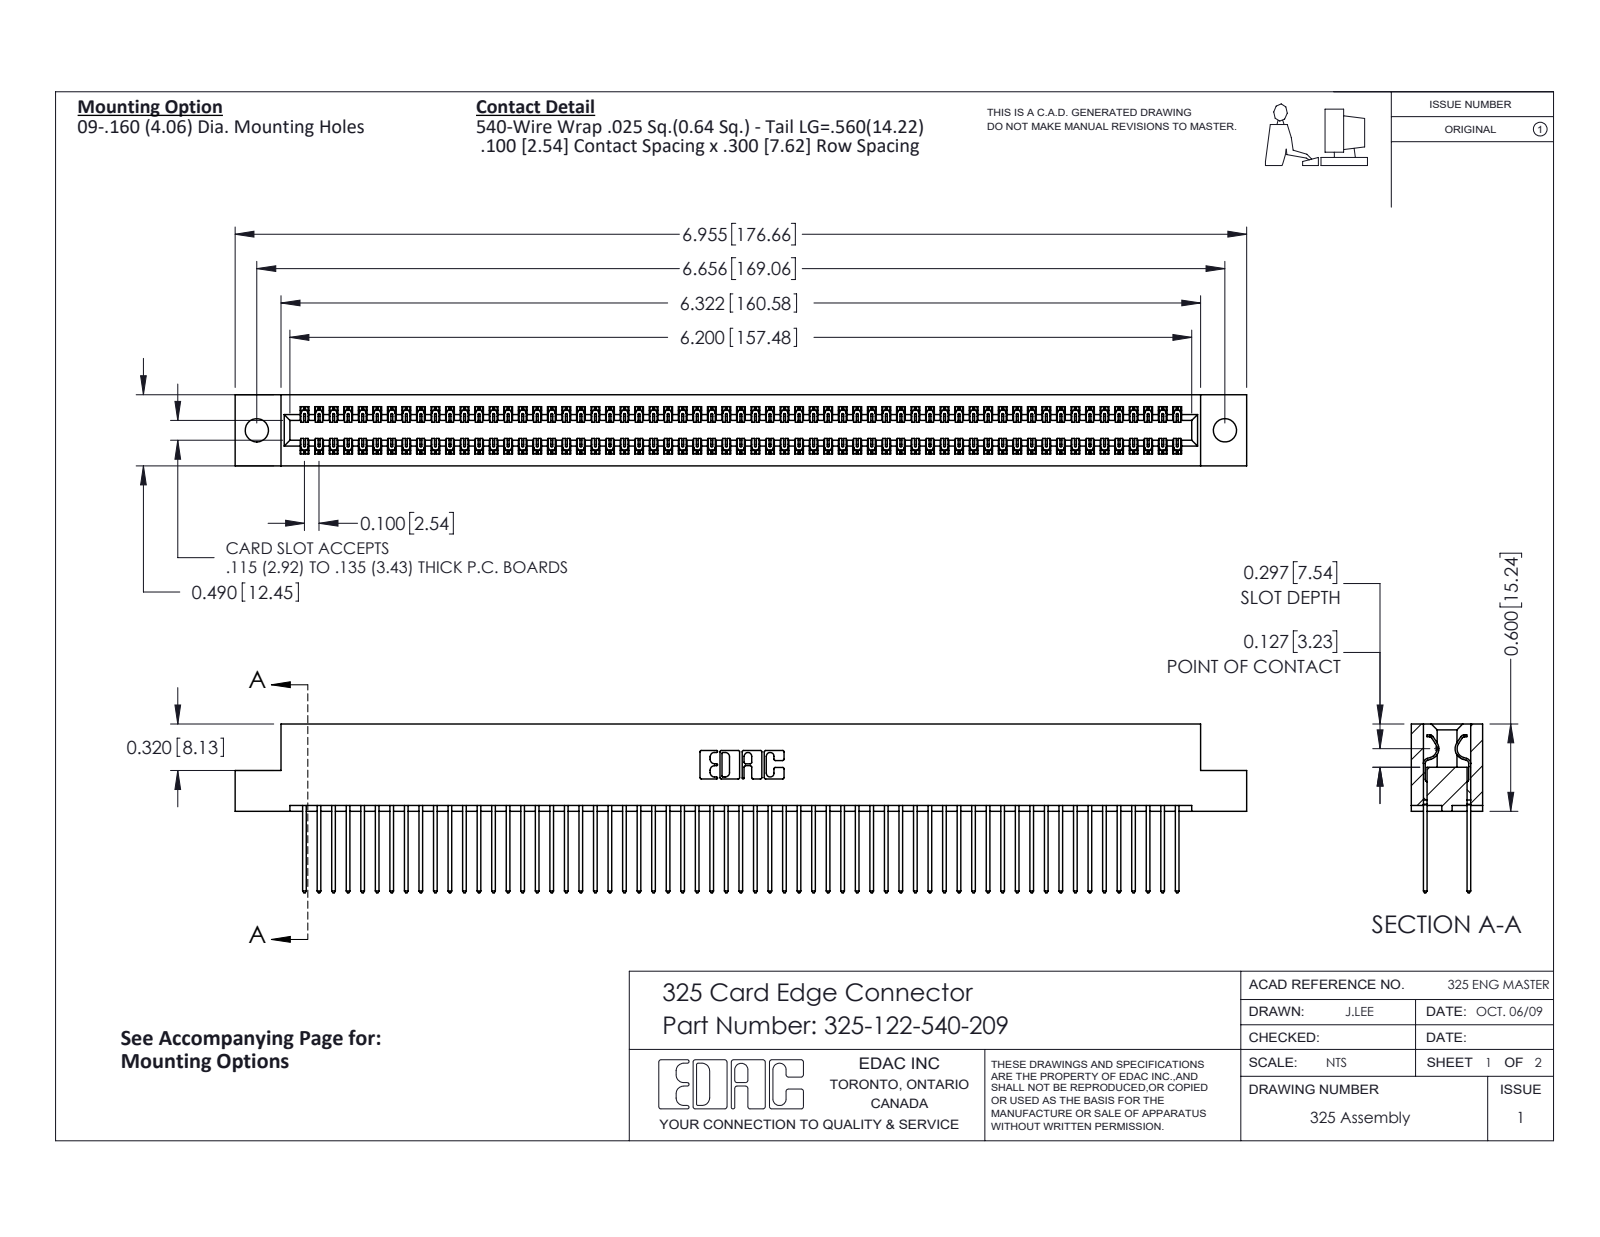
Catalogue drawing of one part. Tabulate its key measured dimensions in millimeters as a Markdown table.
| quantity | value |
| --- | --- |
| part name | 325-122-540-209; 325-292-001_325-293-140; 325 Part_.160 TH |
| STEP written by | SolidWorks 2016 (CONFIG_CONTROL_DESIGN) |
| units | millimeters |
| bodies | 123 solids, 6458 faces (4462 planar, 1996 cylindrical, 0 other) |
| overall size | 176.7 × 29.5 × 12.4 |
| volume | 23 200 mm³ |
| surface area | 30 660 mm² |
| round holes (diameter × count) | 4.1 × 2 |
| partial cylindrical surfaces (radius × count) | 0.2 × 183, 0.3 × 122, 0.3 × 22, 0.2 × 6, 0.8 × 6, 0.7 × 3, 0.4 × 2, 0.6 × 2 |
| main face-to-face distances | 2.1, 10.3, 2.7, 9.7, 0.6, 7.6, 8.3, 12.4, 7, 14.2 |
| hole center spacings | 169.1 |
